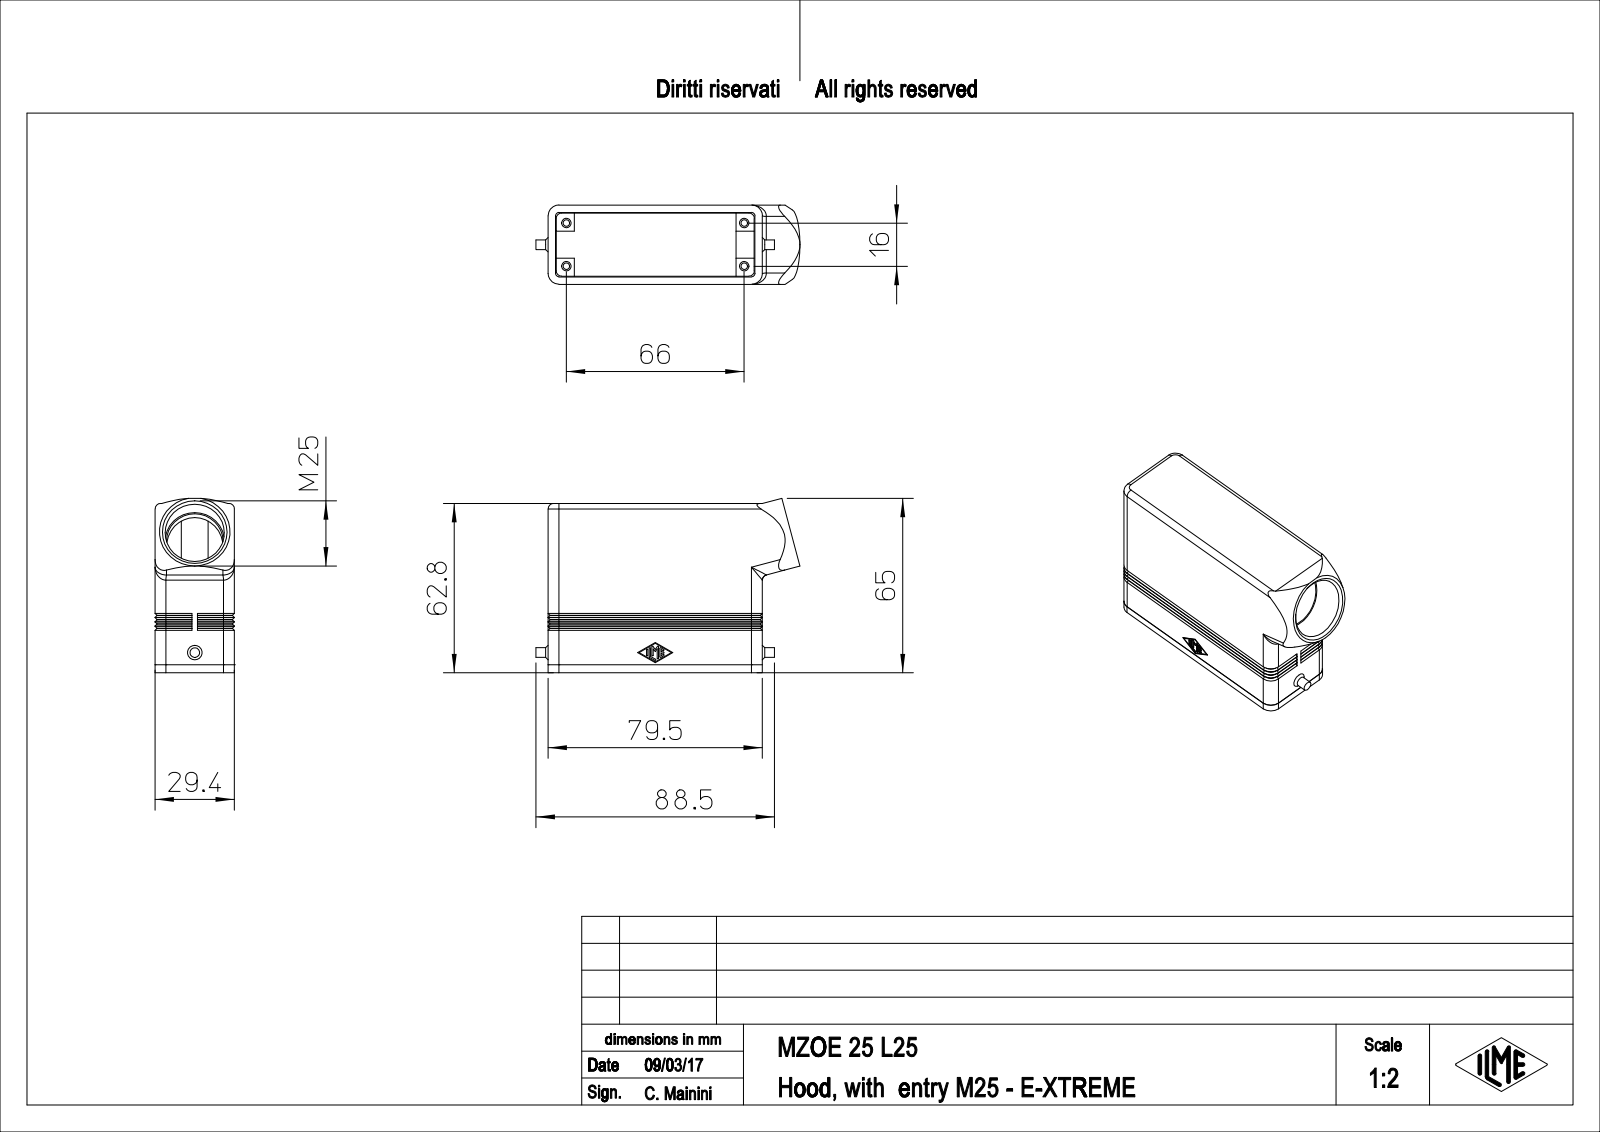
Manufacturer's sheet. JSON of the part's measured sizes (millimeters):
{"part_name": "MZOE_25_L25", "step_written_by": "PTC Creo Elements/Direct Modeling 19.0E 27-Jun-2016 (C) Parametric Technology GmbH (AUTOMOTIVE_DESIGN)", "units": "millimeters", "bodies": {"solids": 1, "faces": 320, "planar": 176, "cylindrical": 91, "other": 53}, "overall_size": [98.01, 64.75, 29.41], "volume_mm3": 52310, "surface_area_mm2": 31501, "round_holes": [[2.46, 4], [3.5, 4], [21, 1], [22, 1]], "round_bosses_or_shafts": [[3.6, 1]], "partial_cylinders_radius": [[0.25, 14], [4, 8], [2, 7], [1.25, 4], [3.3, 4], [4.2, 2]], "face_to_face_distances": [3, 26.4, 29.4, 23.4, 9.75, 69.75, 6.75, 76.5, 66.75, 1.13], "hole_center_spacings": [16, 66, 67.91]}
